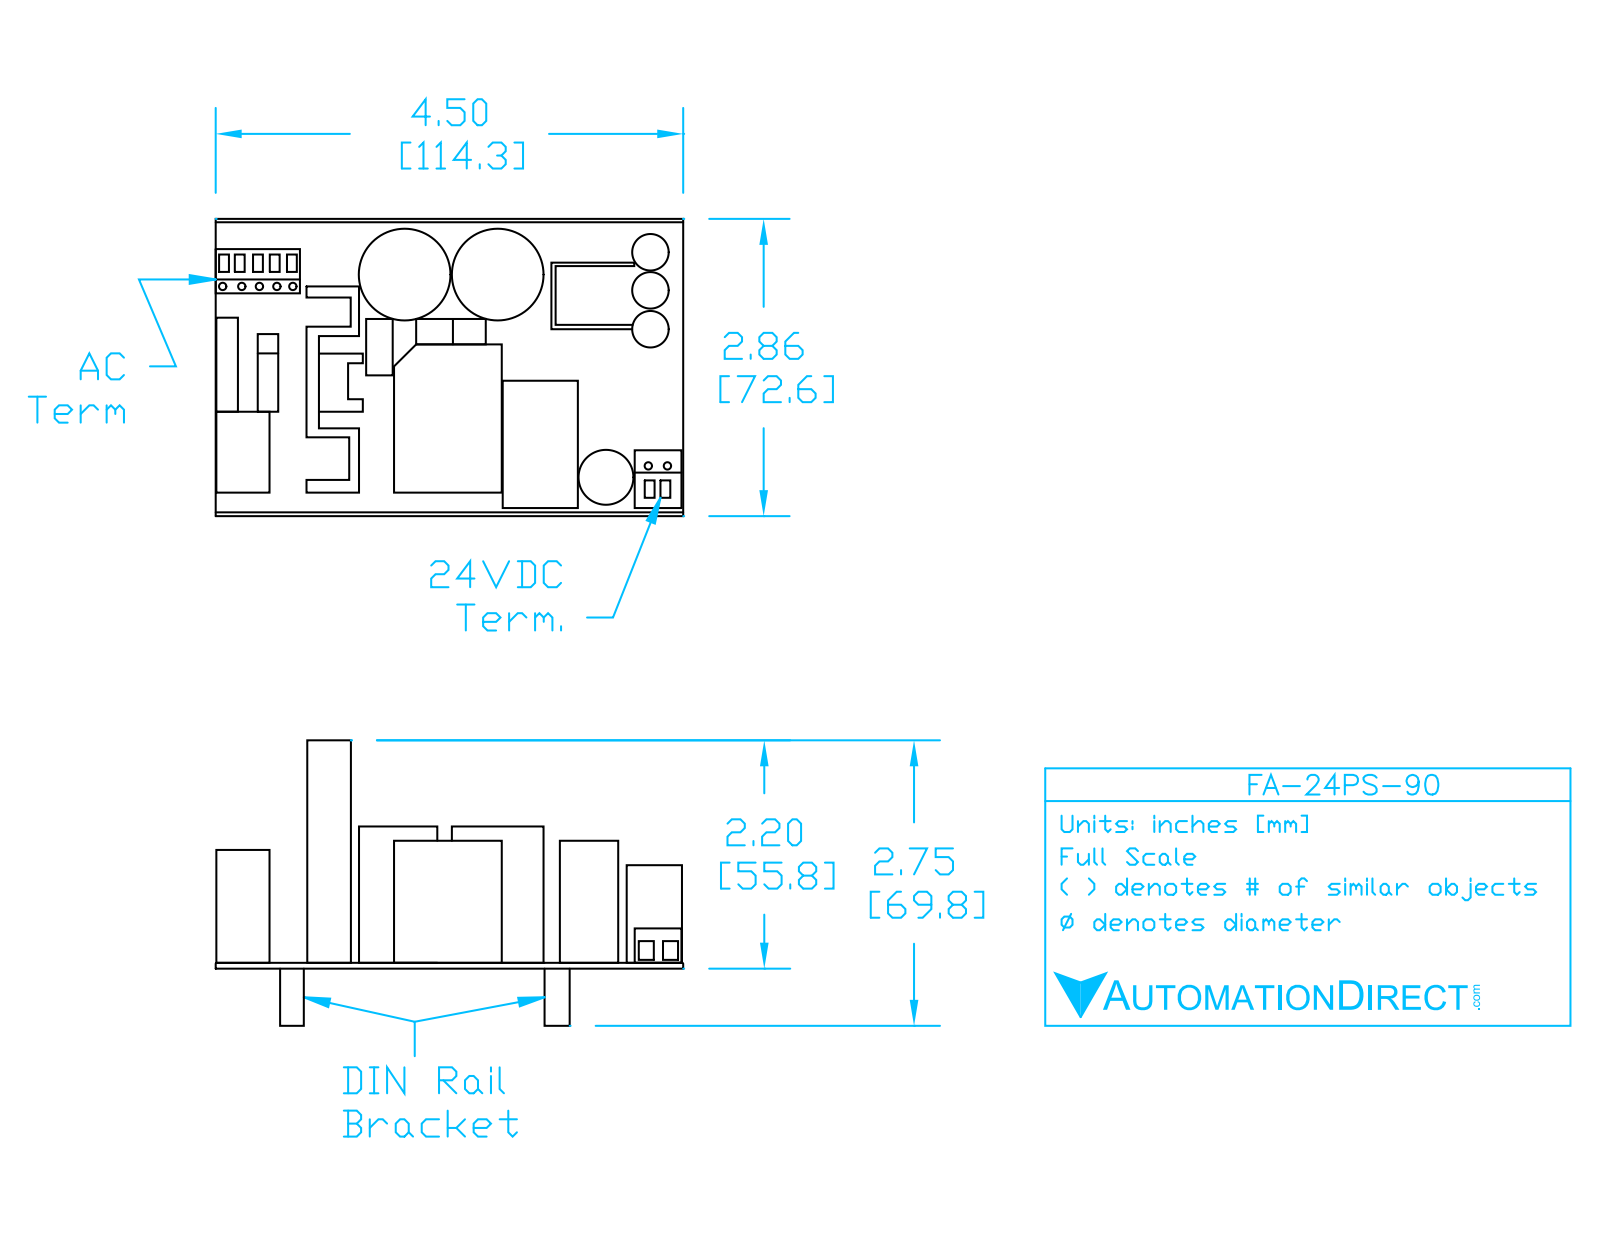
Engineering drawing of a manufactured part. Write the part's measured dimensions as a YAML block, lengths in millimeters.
part_name: "FA-24PS-90"
step_written_by: "SolidWorks 2011 (CONFIG_CONTROL_DESIGN)"
units: millimeters
bodies: {solids: 1, faces: 878, planar: 617, cylindrical: 203, other: 58}
overall_size: [125.9, 86.9, 76.6]
volume: 237800
surface_area: 63990
round_holes:
  - {diameter: 3, count: 7}
  - {diameter: 5.7, count: 2}
round_bosses_or_shafts:
  - {diameter: 12.7, count: 3}
  - {diameter: 1, count: 3}
  - {diameter: 21.6, count: 2}
  - {diameter: 5.2, count: 2}
  - {diameter: 9.5, count: 1}
  - {diameter: 8.8, count: 1}
  - {diameter: 2.8, count: 1}
partial_cylinders:
  - {radius: 0.4, count: 41}
  - {radius: 0.8, count: 10}
  - {radius: 3, count: 6}
  - {radius: 1, count: 4}
  - {radius: 1.5, count: 2}
  - {radius: 5.1, count: 2}
face_to_face_distances: [16, 2, 31.6, 10.7, 0.8, 124.5, 16.7, 12.7, 1.4, 33.6]
hole_center_spacings: [5.1, 10.2, 15.2, 20.3, 72.4]
